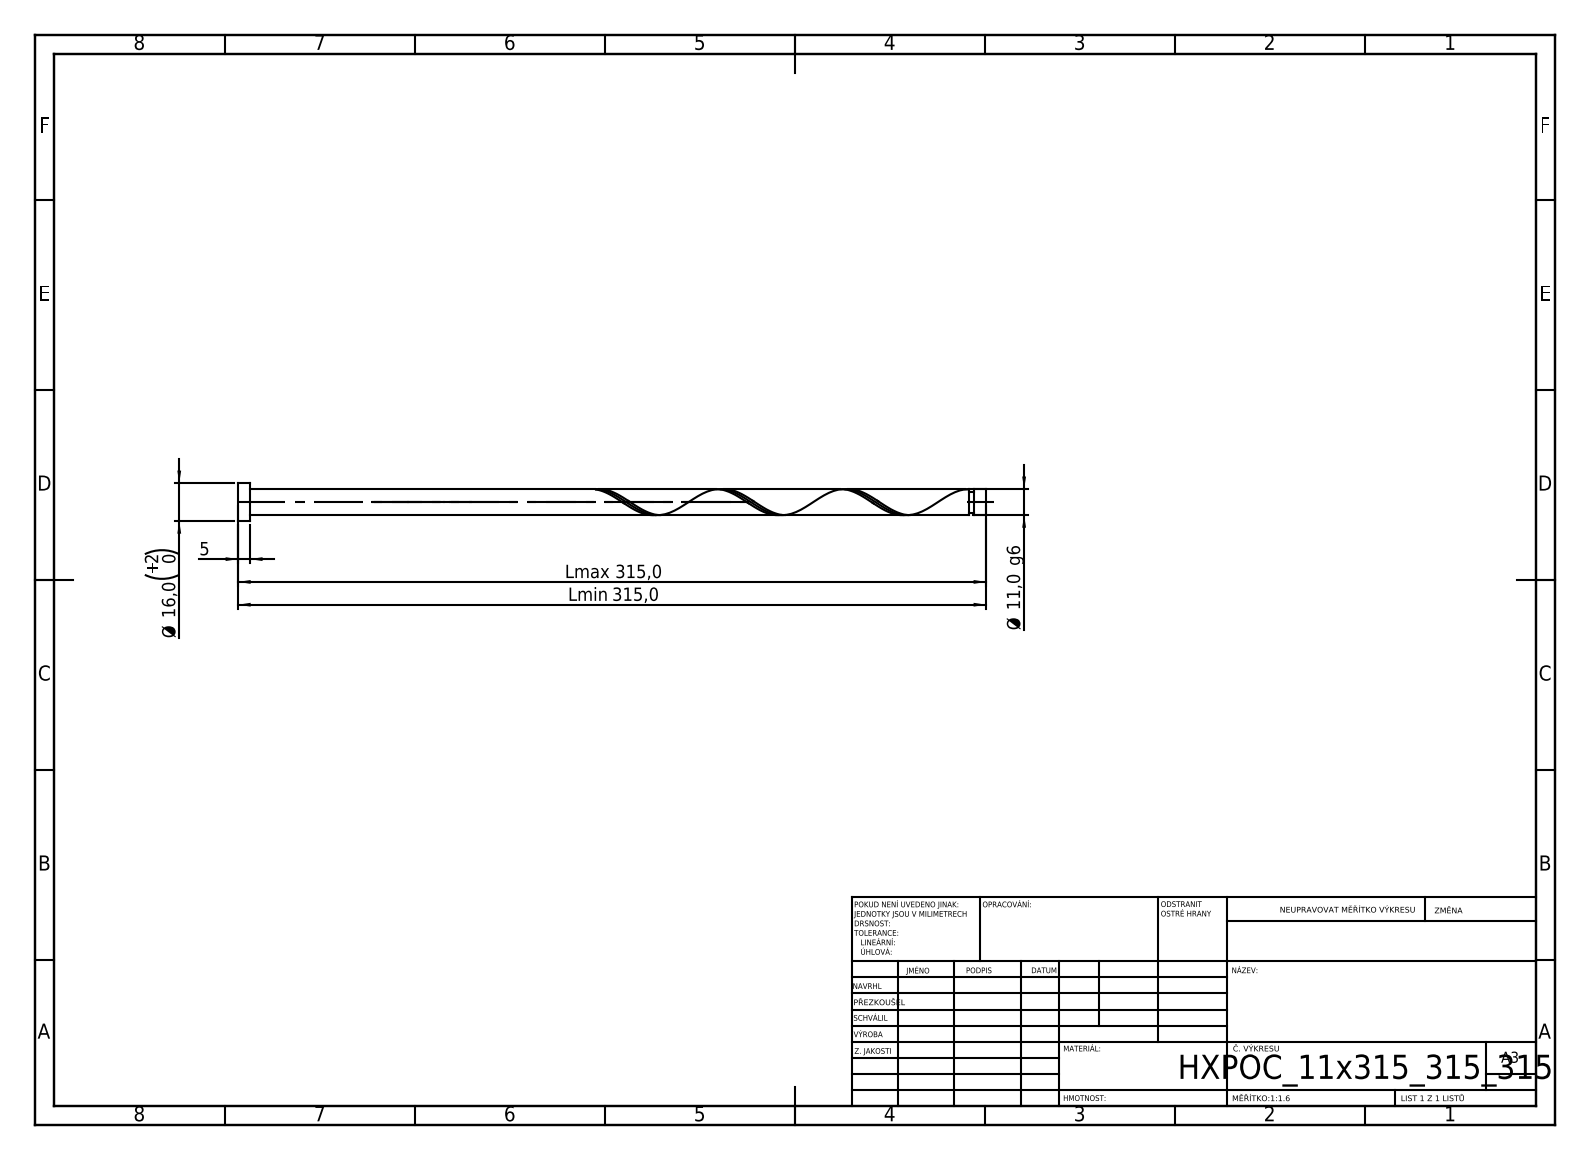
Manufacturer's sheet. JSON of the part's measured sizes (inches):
{"step_written_by": "SolidWorks 2019 (CONFIG_CONTROL_DESIGN)", "units": "inches", "bodies": {"solids": 1, "faces": 21, "planar": 6, "cylindrical": 14, "other": 1}, "overall_size": [12.402, 0.63, 0.63], "volume_in3": 1.837, "surface_area_in2": 18.03, "round_bosses_or_shafts": [[0.63, 1], [0.433, 1], [0.346, 1]], "face_to_face_distances": [0.197, 12.205, 12.402, 12.008, 12.118, 11.921, 0.087, 0.283, 5.917, 5.72]}
